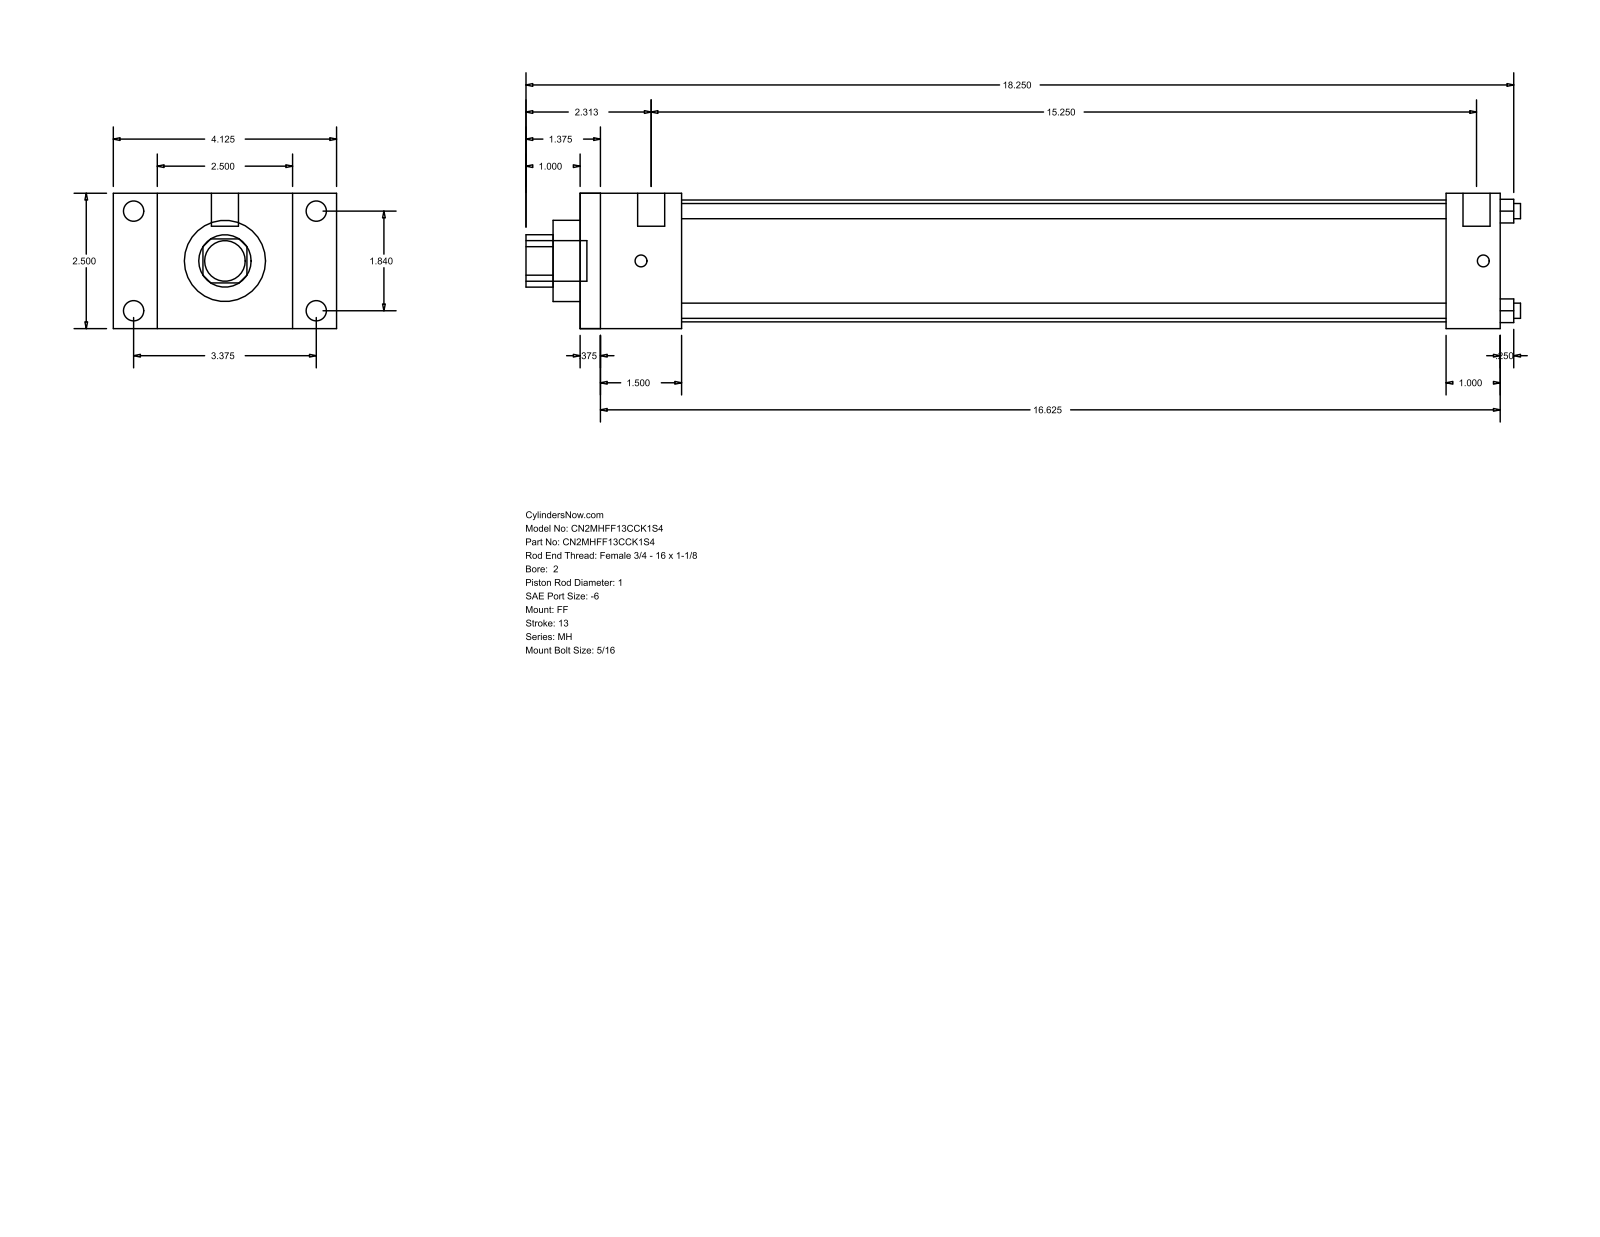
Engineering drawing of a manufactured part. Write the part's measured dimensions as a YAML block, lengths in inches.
part_name: "MH_FF__0200_1"
step_written_by: "GSSL Pune (CONFIG_CONTROL_DESIGN)"
units: inches
bodies: {solids: 0, faces: 92, planar: 64, cylindrical: 28, other: 0}
overall_size: [18.375, 4.125, 2.5]
round_holes:
  - {diameter: 0.281, count: 4}
  - {diameter: 1, count: 1}
  - {diameter: 1.5, count: 1}
  - {diameter: 2.25, count: 1}
round_bosses_or_shafts:
  - {diameter: 0.375, count: 4}
  - {diameter: 0.219, count: 4}
  - {diameter: 0.5, count: 2}
  - {diameter: 0.75, count: 1}
partial_cylinders:
  - {radius: 0.484, count: 1}
face_to_face_distances: [2.5, 17, 0.375, 16.625, 0.813, 1, 1.875, 16, 1.5, 15.625]
hole_center_spacings: [1.301, 1.84, 2.602]
